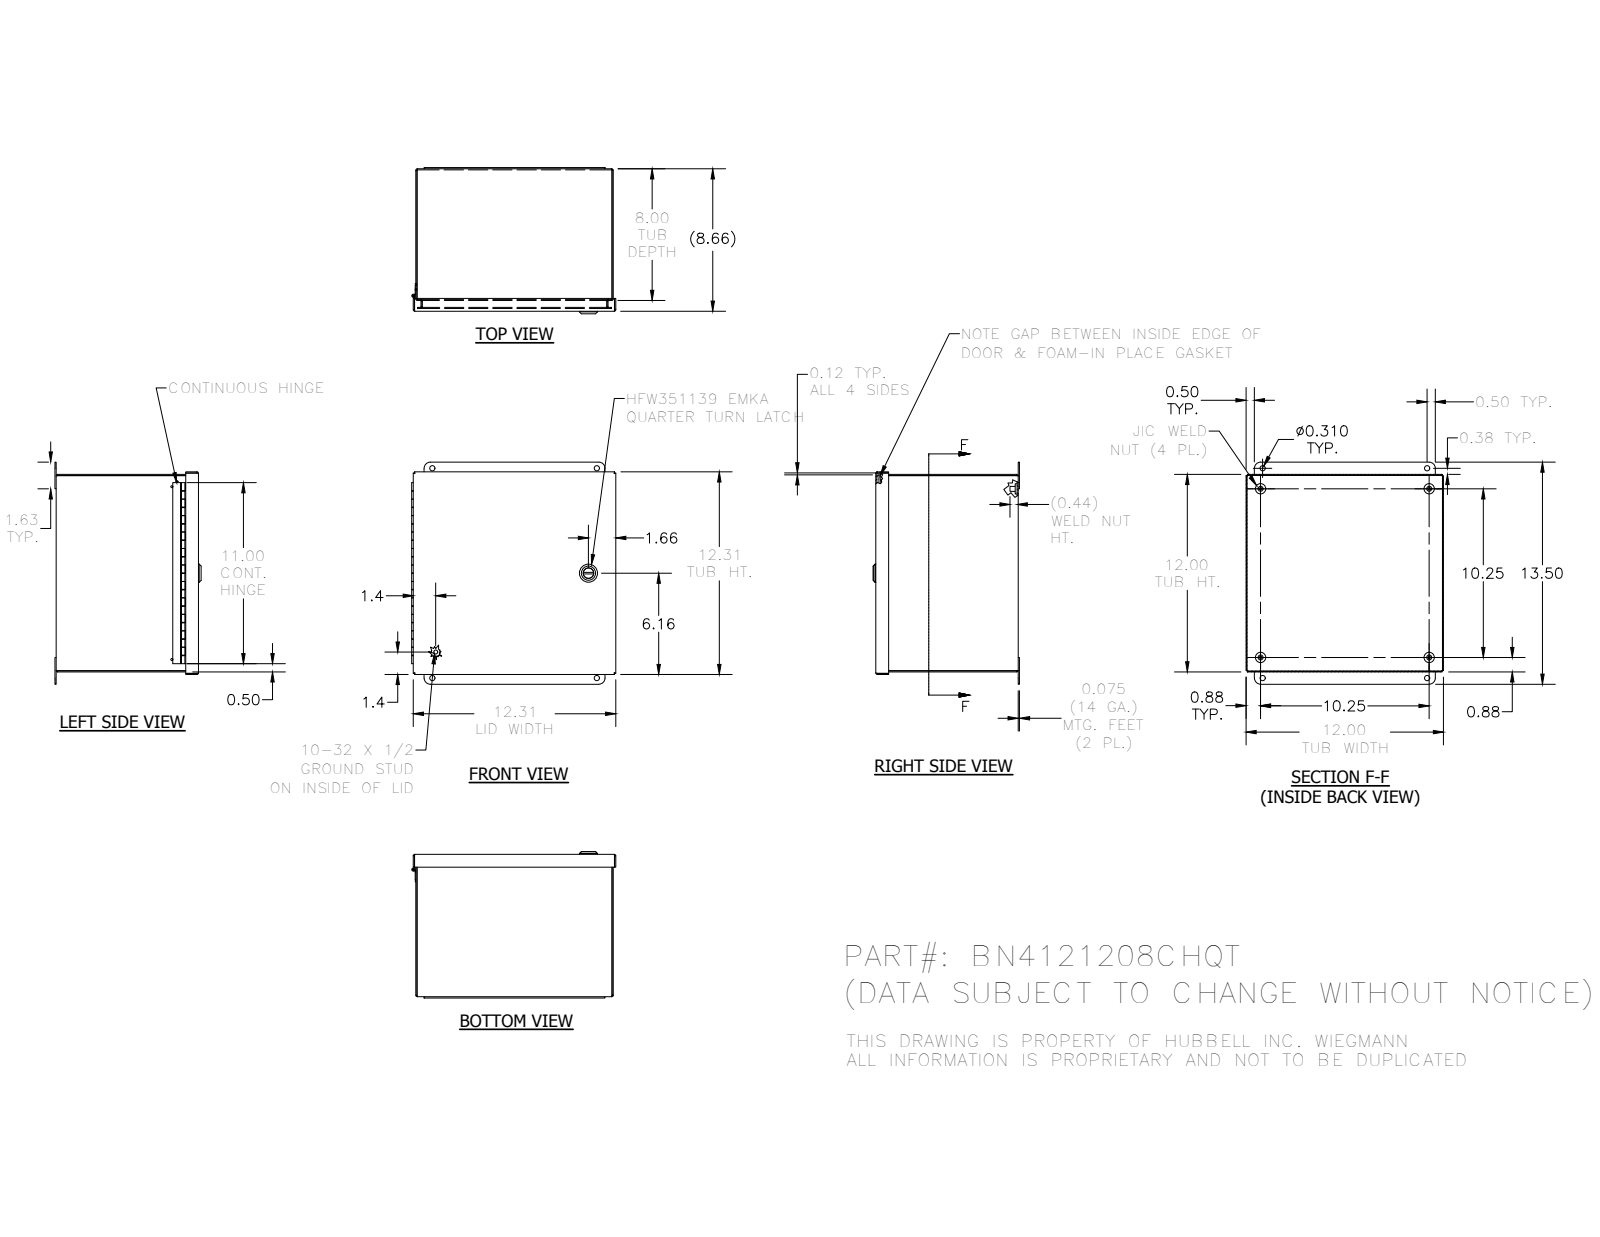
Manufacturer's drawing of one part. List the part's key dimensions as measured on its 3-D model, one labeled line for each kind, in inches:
Part name (STEP PRODUCT): BN4121208CHQT
STEP written by: SolidWorks 2018 (AUTOMOTIVE_DESIGN)
Units: inches
Bodies: 21 solids, 785 faces (396 planar, 261 cylindrical, 128 other)
Overall size (bounding box): 13.5 × 12.406 × 8.888
Volume: 55.23 in³ · Surface area: 1 700 in²
Round holes (diameter × count): ⌀0.156 ×4, ⌀0.31 ×4, ⌀0.12 ×3, ⌀0.116 ×1, ⌀0.197 ×1, ⌀0.315 ×1, ⌀0.394 ×1, ⌀0.402 ×1, ⌀0.634 ×1, ⌀0.802 ×1
Round bosses / shafts (diameter × count): ⌀0.625 ×4, ⌀0.3 ×4, ⌀1.102 ×1, ⌀0.866 ×1, ⌀0.78 ×1, ⌀0.622 ×1, ⌀0.598 ×1, ⌀0.531 ×1
Partial cylindrical surfaces — rounded edges, fillets, slot ends (radius × count): R0.012 ×30, R0.031 ×20, R0.093 ×20, R0.125 ×16, R0.02 ×12, R0.157 ×4, R0.375 ×4, R0.016 ×2
Main face-to-face distances: 0.062, 0.062, 11.938, 12, 8.594, 8.656, 8.532, 8.594, 11.876, 11.938
Hole centre spacings: 10.25, 15.322, 1.256, 10, 10.202, 10.202, 10.9, 11.501
